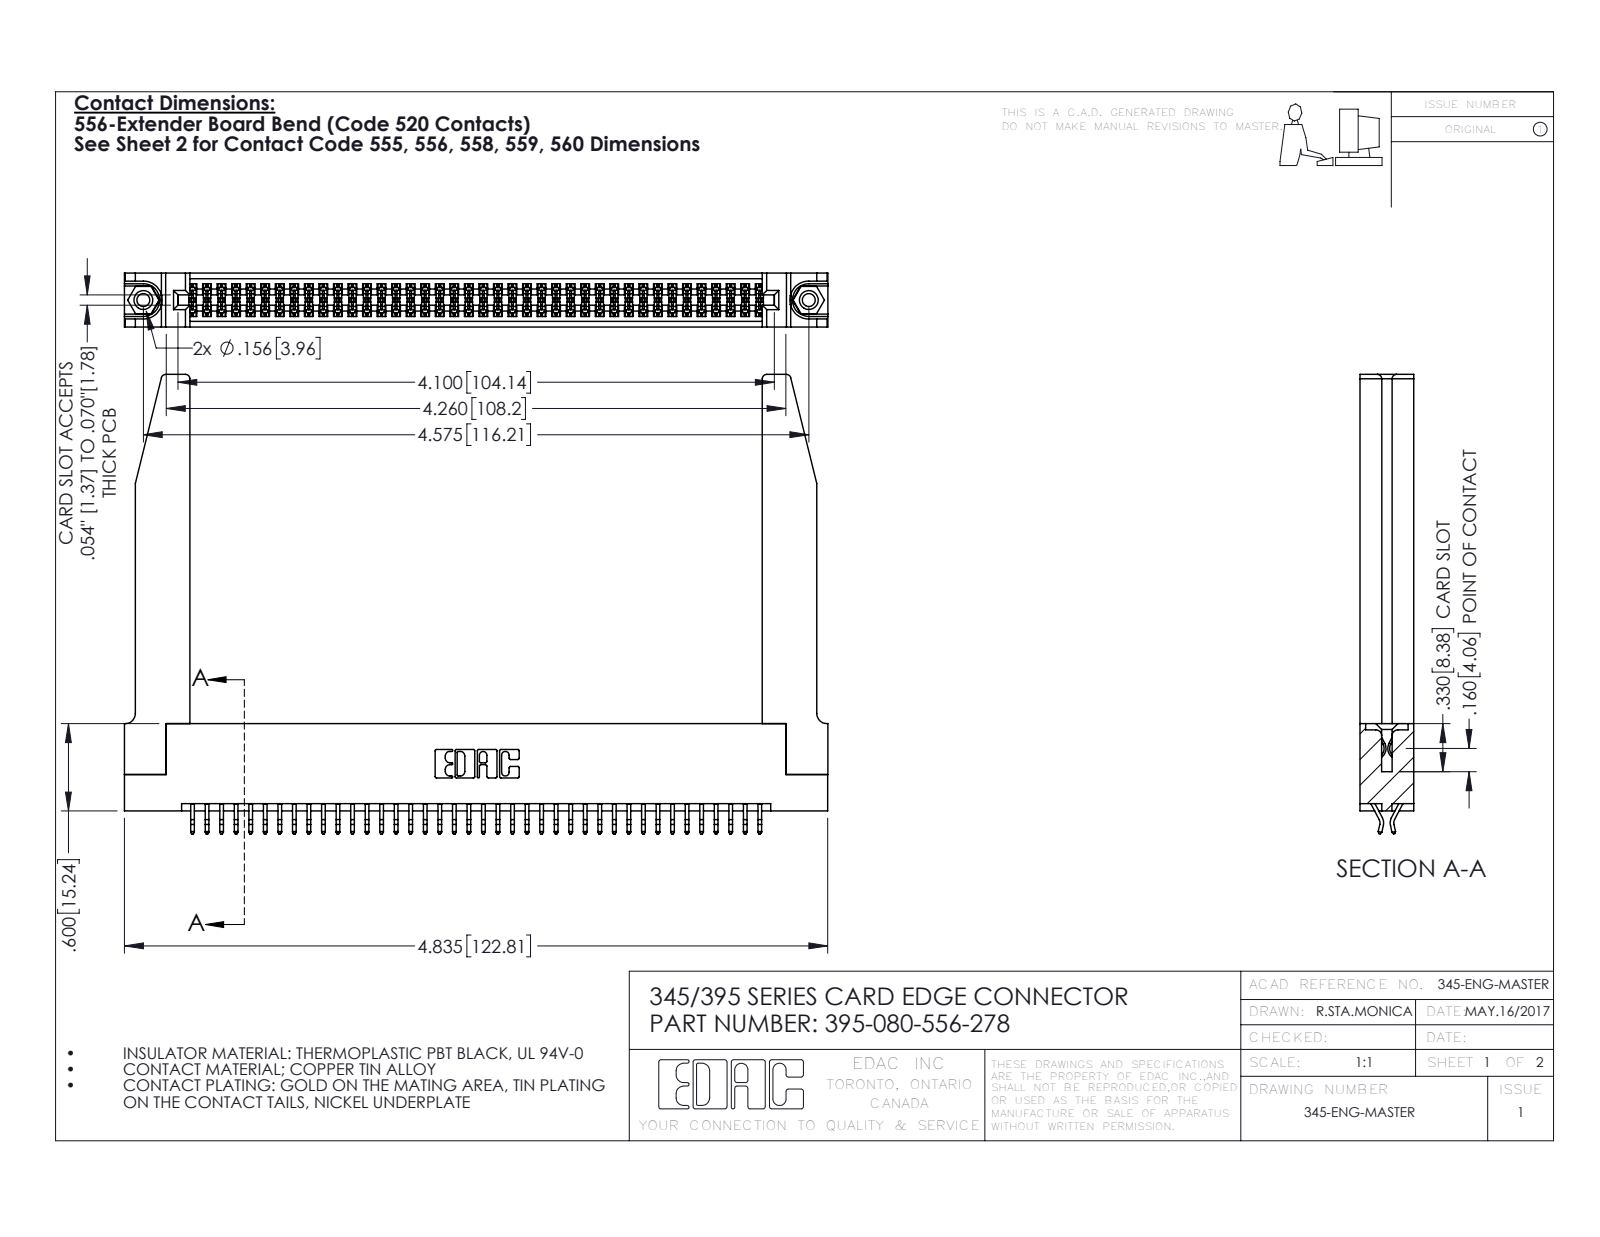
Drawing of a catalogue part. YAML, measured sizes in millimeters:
part_name: "345-220-078_345-220-078; 345-292-001_556 Tail; 345-250-001_345-250-001-102; 345 Part_Flush Mounting Lugs - 0.156 Dia-TH (+1 more)"
step_written_by: "SolidWorks 2016 (CONFIG_CONTROL_DESIGN)"
units: millimeters
bodies: {solids: 85, faces: 4840, planar: 3182, cylindrical: 1606, other: 52}
overall_size: [122.8, 80.2, 9.4]
volume: 19680
surface_area: 24340
round_holes:
  - {diameter: 2.3, count: 2}
  - {diameter: 3.2, count: 2}
  - {diameter: 4, count: 2}
  - {diameter: 1.6, count: 1}
round_bosses_or_shafts:
  - {diameter: 3.9, count: 2}
partial_cylinders:
  - {radius: 0.2, count: 120}
  - {radius: 0.3, count: 22}
  - {radius: 0.8, count: 8}
  - {radius: 0.2, count: 6}
  - {radius: 0.8, count: 6}
  - {radius: 0.7, count: 3}
  - {radius: 0.3, count: 2}
  - {radius: 0.4, count: 2}
face_to_face_distances: [9.4, 1.8, 7.6, 5.1, 0.6, 2.5, 6.9, 5.7, 3.8, 3.8]
hole_center_spacings: [6.9, 110.2, 116.2]
